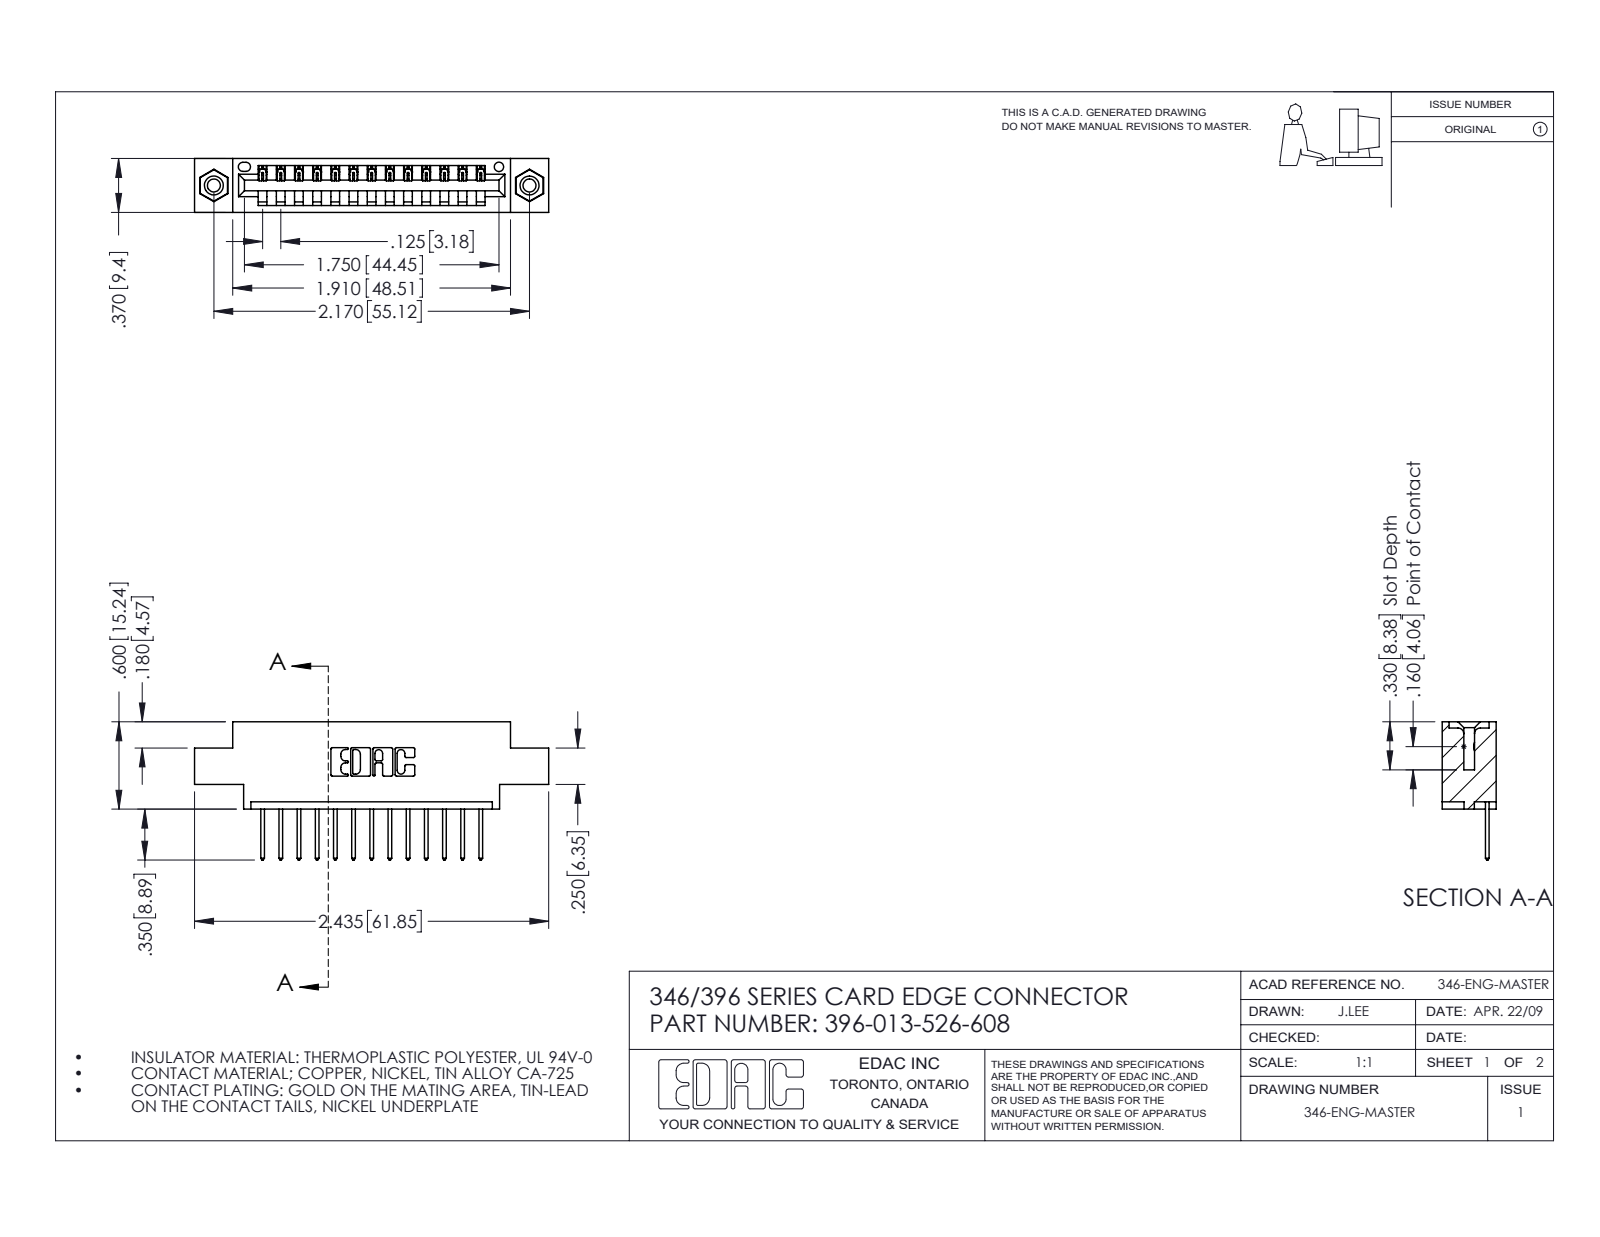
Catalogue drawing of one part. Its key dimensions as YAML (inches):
part_name: "396-013-526-608; 346 Part_0.170 Offset - 0.156 Dia-TI; 345-292-001_345-293-126; 345-250-001_345-250-003-102"
step_written_by: "SolidWorks 2016 (CONFIG_CONTROL_DESIGN)"
units: inches
bodies: {solids: 16, faces: 940, planar: 632, cylindrical: 292, other: 16}
overall_size: [2.435, 0.95, 0.37]
volume: 0.339
surface_area: 10.53
round_holes:
  - {diameter: 0.089, count: 2}
  - {diameter: 0.125, count: 2}
  - {diameter: 0.156, count: 2}
  - {diameter: 0.064, count: 1}
round_bosses_or_shafts:
  - {diameter: 0.155, count: 2}
partial_cylinders:
  - {radius: 0.006, count: 26}
  - {radius: 0.01, count: 26}
  - {radius: 0.01, count: 22}
  - {radius: 0.007, count: 6}
  - {radius: 0.031, count: 6}
  - {radius: 0.026, count: 3}
  - {radius: 0.031, count: 2}
  - {radius: 0.04, count: 2}
face_to_face_distances: [0.25, 0.37, 0.048, 0.322, 0.072, 0.298, 0.025, 0.222, 0.148, 0.1]
hole_center_spacings: [0.246, 1.964, 2.17]
